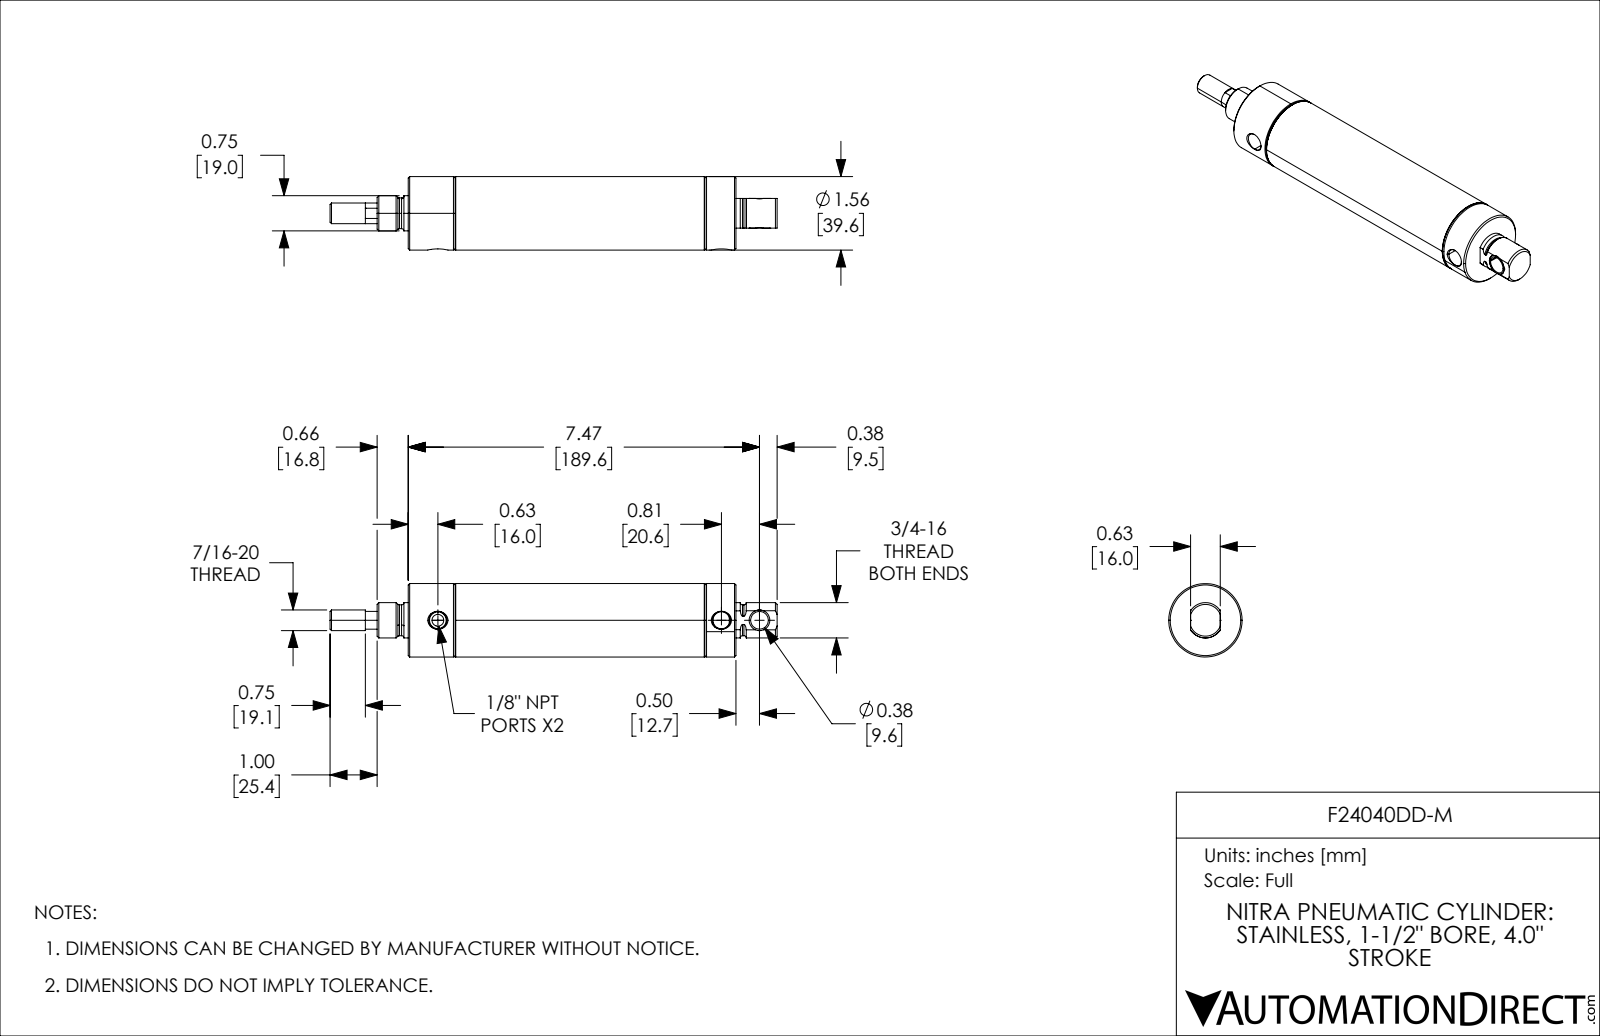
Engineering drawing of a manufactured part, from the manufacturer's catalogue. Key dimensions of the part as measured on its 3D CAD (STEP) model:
Part name (STEP PRODUCT): F24040DD-M_9; F24040DD-M_5; F24040DD-M; F24040DD-M_11 (+2 more)
STEP written by: SolidWorks 2021 (CONFIG_CONTROL_DESIGN)
Units: millimetres
Bodies: 5 solids, 157 faces (35 planar, 58 cylindrical, 64 other)
Overall size (bounding box): 241.3 × 39.62 × 39.62
Volume: 113 158 mm³ · Surface area: 64 064 mm²
Round holes (diameter × count): ⌀6.35 ×1, ⌀9.14 ×1, ⌀9.55 ×1, ⌀11.15 ×1, ⌀11.73 ×1, ⌀13.51 ×1, ⌀26.97 ×1, ⌀36.36 ×1
Round bosses / shafts (diameter × count): ⌀39.62 ×1, ⌀38.39 ×1, ⌀19.05 ×1, ⌀18.99 ×1, ⌀16.61 ×1, ⌀16.6 ×1, ⌀11.13 ×1, ⌀11.11 ×1
Main face-to-face distances: 22.22, 44.45, 101.6, 123.82, 146.05, 22.23, 30.86, 132.46, 154.68, 176.91
Hole centre spacings: 20.57, 153.04, 173.61
